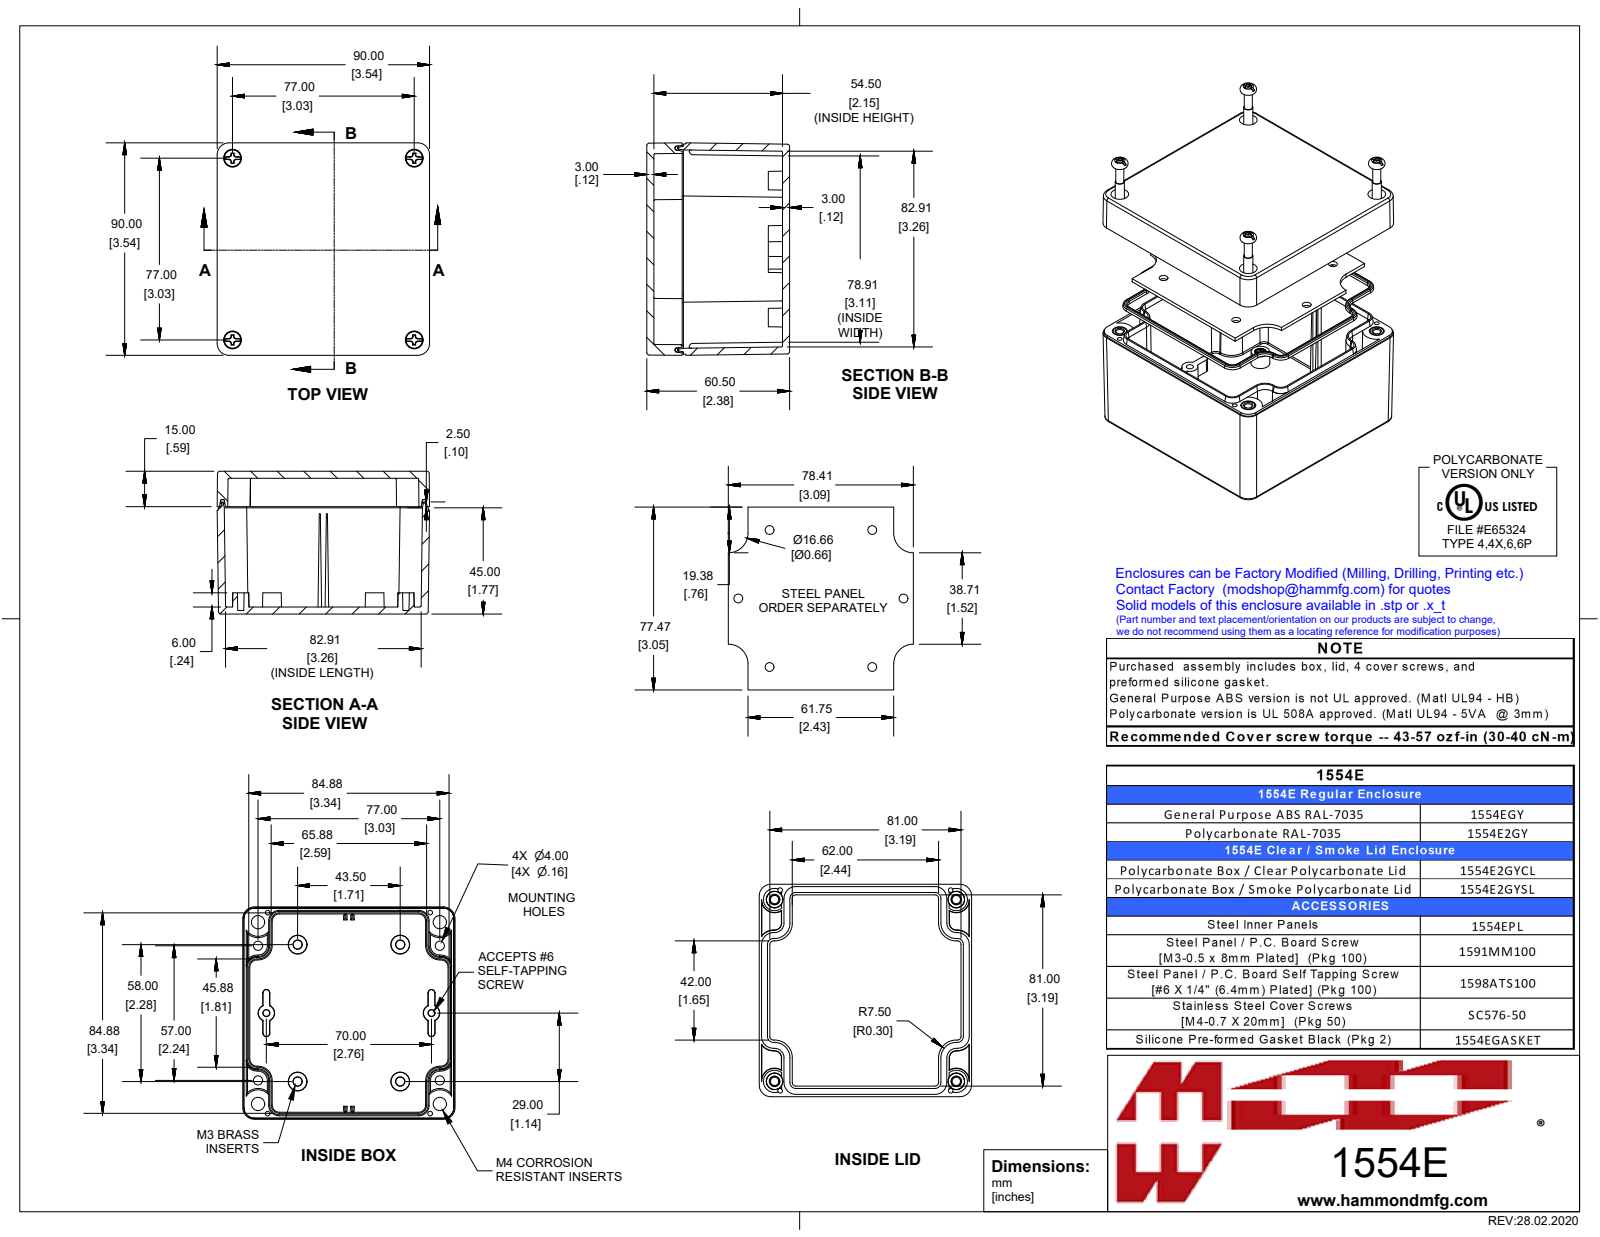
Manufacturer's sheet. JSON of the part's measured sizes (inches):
{"part_name": "1554EGY", "step_written_by": "SolidWorks 2019 (AUTOMOTIVE_DESIGN)", "units": "inches", "bodies": {"solids": 16, "faces": 1330, "planar": 366, "cylindrical": 338, "other": 626}, "overall_size": [3.543, 3.543, 2.382], "volume_in3": 8.154, "surface_area_in2": 162.6, "round_holes": [[0.079, 8], [0.097, 4], [0.128, 4], [0.138, 4], [0.147, 4], [0.276, 4], [0.11, 2]], "round_bosses_or_shafts": [[0.25, 4], [0.218, 4], [0.21, 4], [0.19, 4], [0.154, 4], [0.153, 4], [0.15, 4], [0.135, 4]], "partial_cylinders_radius": [[0.02, 32], [0.039, 8], [0.197, 8], [0.187, 4], [0.328, 4], [0.059, 2]], "face_to_face_distances": [0.118, 2.264, 2.382, 0.354, 1.909, 0.236, 2.028, 2.146, 0.059, 0.419], "hole_center_spacings": [1.255, 2.276, 2.401, 2.509, 2.738, 2.861, 3.562, 3.582]}
